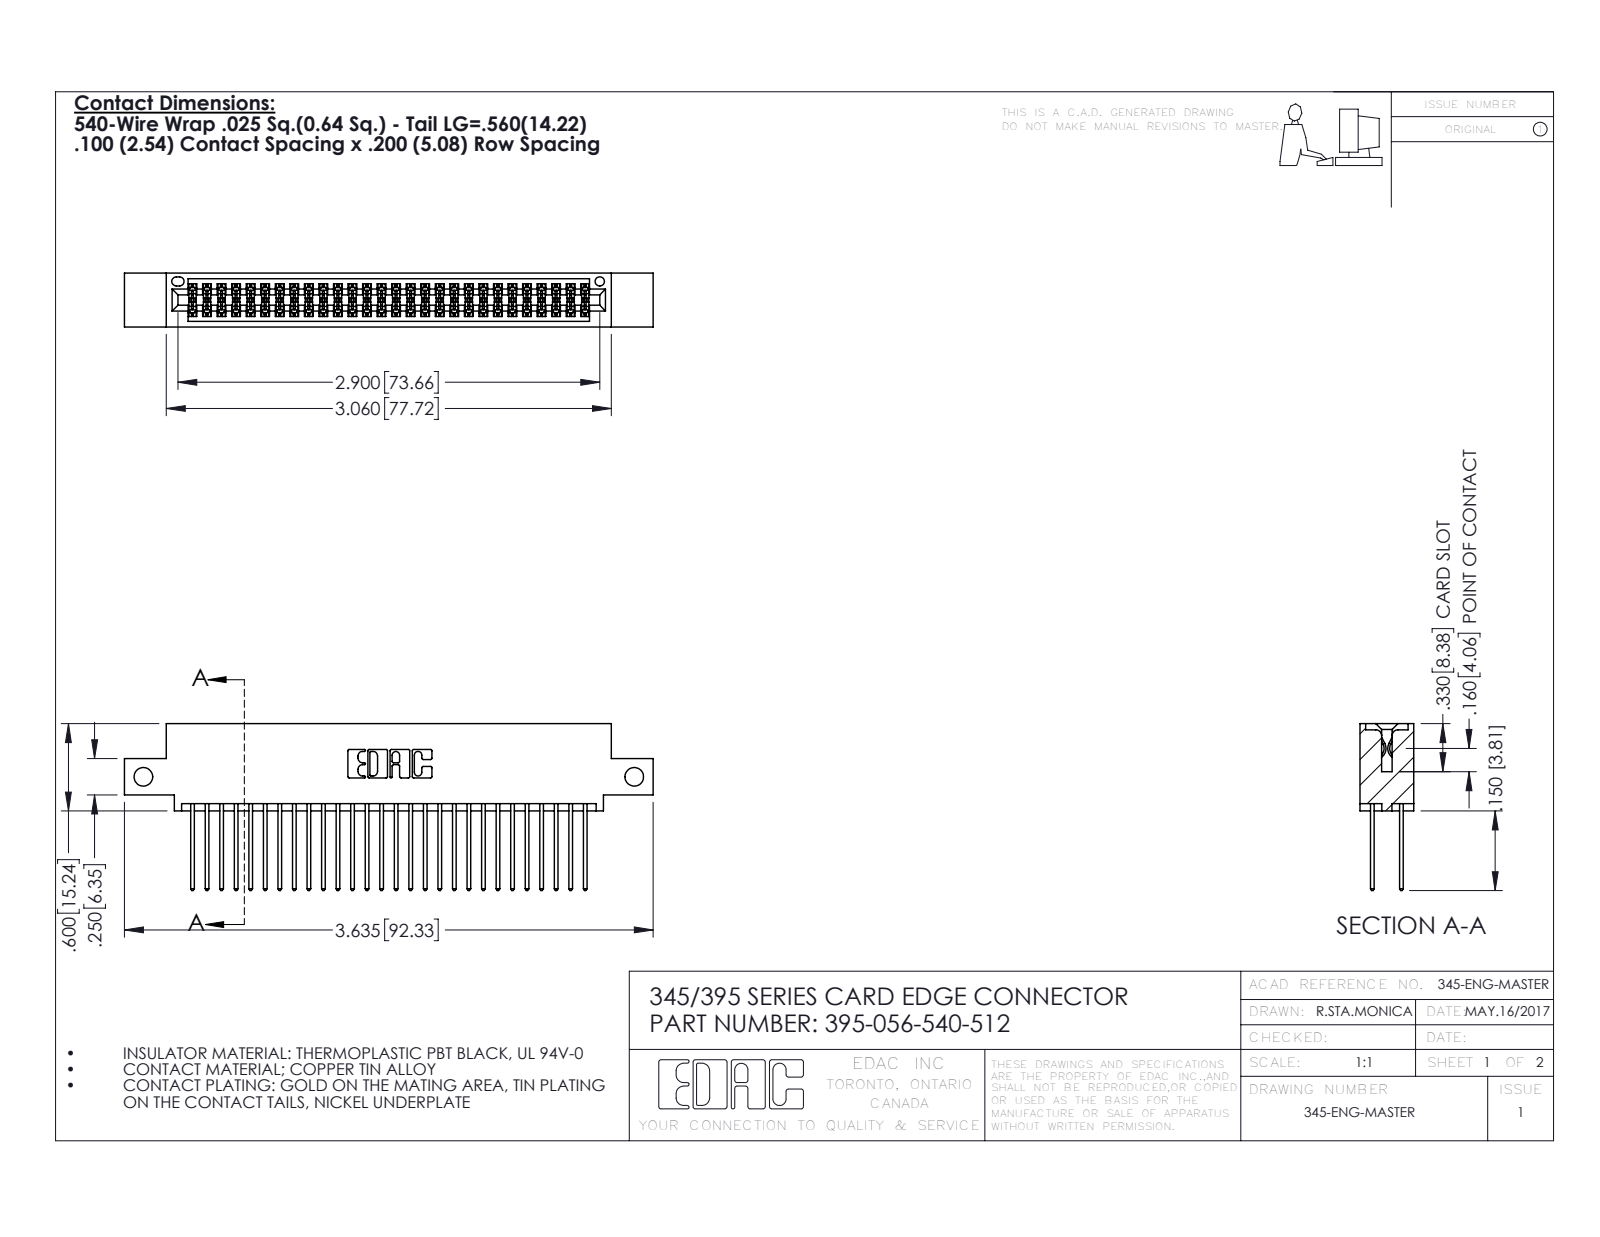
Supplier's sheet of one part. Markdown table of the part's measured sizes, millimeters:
| quantity | value |
| --- | --- |
| part name | 345 Part_0.110 Offset - Side Mount; 345-292-001_345-293-140; 395-056-540-512 |
| STEP written by | SolidWorks 2016 (CONFIG_CONTROL_DESIGN) |
| units | millimeters |
| bodies | 57 solids, 2930 faces (1932 planar, 998 cylindrical, 0 other) |
| overall size | 92.3 × 29.1 × 9.4 |
| volume | 8 900 mm³ |
| surface area | 13 810 mm² |
| round holes (diameter × count) | 3.3 × 2, 1.6 × 1 |
| partial cylindrical surfaces (radius × count) | 0.2 × 84, 0.3 × 56, 0.3 × 22, 0.2 × 6, 0.8 × 6, 0.7 × 3, 0.4 × 2, 0.5 × 2 |
| main face-to-face distances | 1.8, 7.6, 5.1, 2.5, 6.9, 0.6, 9.4, 5.7, 4.4, 3.8 |
| hole center spacings | 85.7 |
